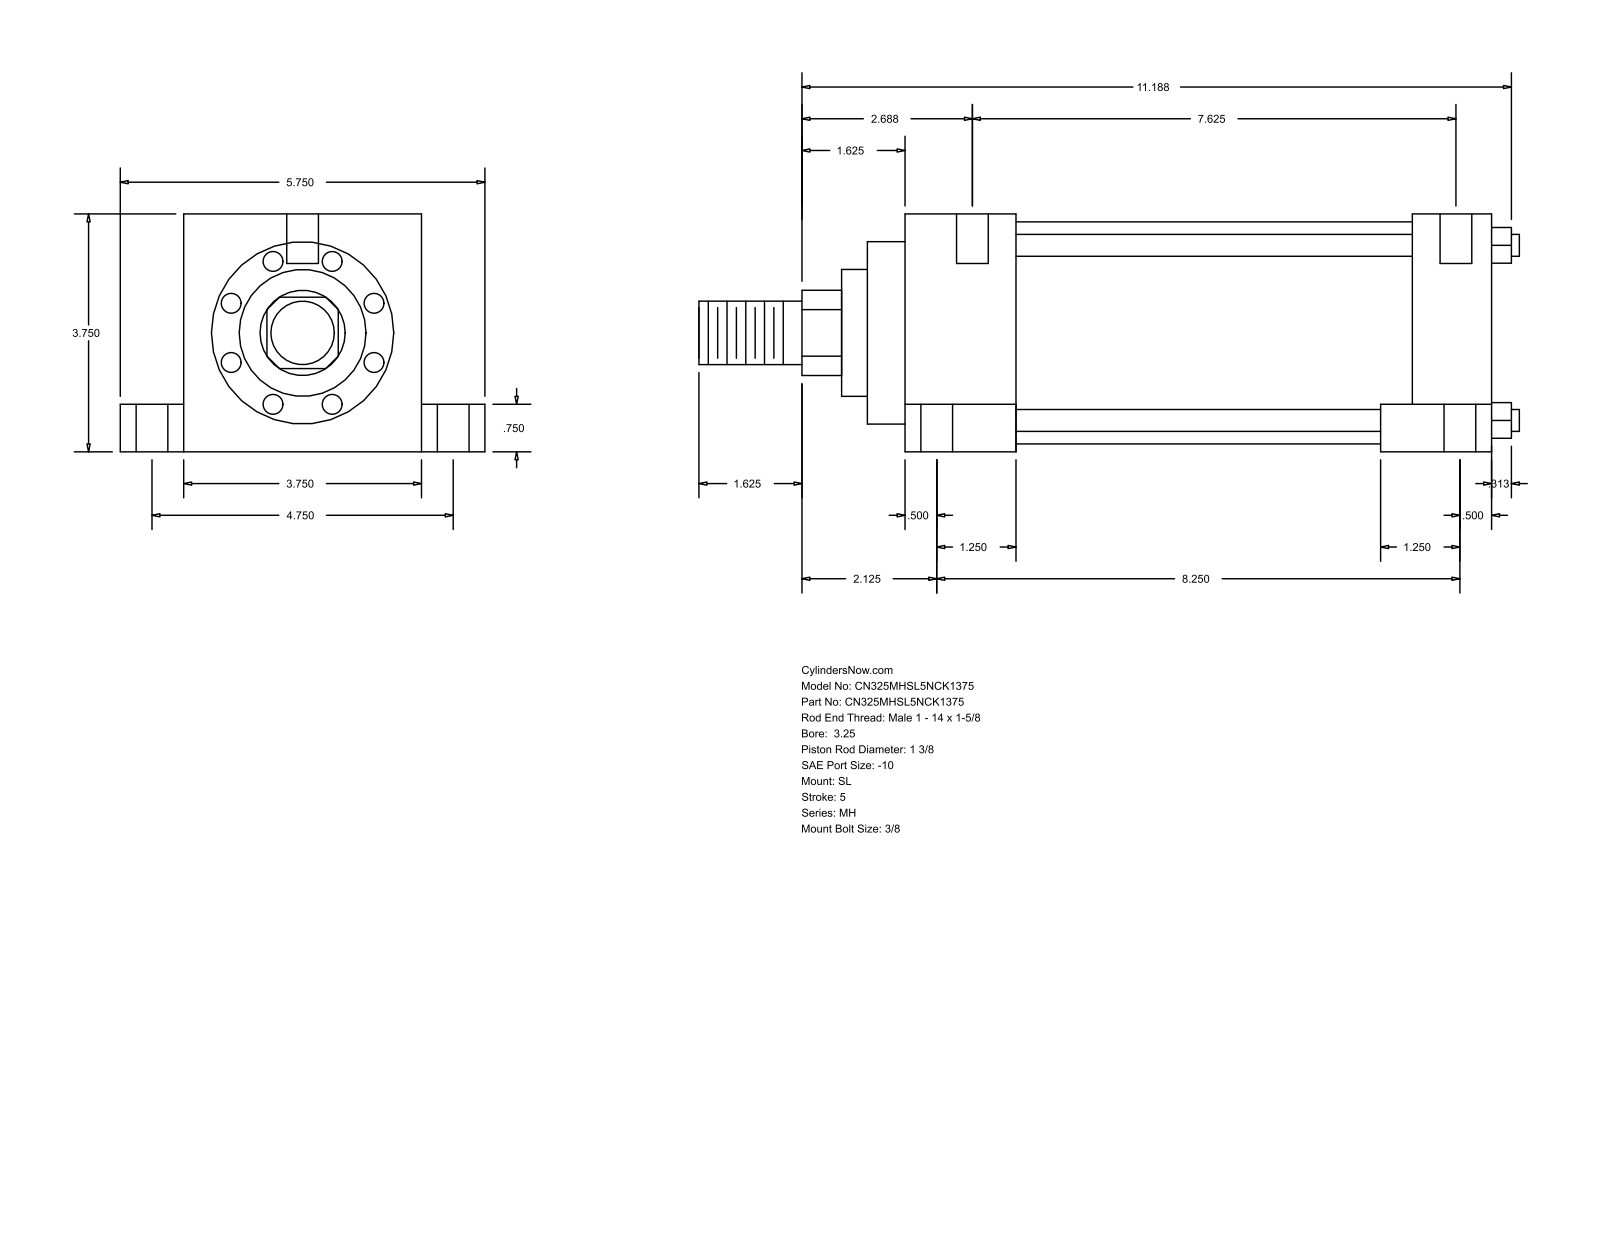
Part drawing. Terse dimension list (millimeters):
name: MH_SL__0325_1.375
written by: GSSL Pune (CONFIG_CONTROL_DESIGN)
unit: mm
bodies: 0 solids, 110 faces (77 planar, 33 cylindrical, 0 other)
size: 328.61 × 146.05 × 95.25
holes: 6× ⌀12.7, 4× ⌀5.56, 4× ⌀19.05
bosses: 4× ⌀8.76, 1× ⌀88.9, 1× ⌀73.03, 1× ⌀50.8, 1× ⌀34.92, 1× ⌀25.4
rounds: 1× R17.06
face distances: 95.24, 234.96, 44.45, 190.51, 25.41, 120.65, 19.05, 76.19, 146.06, 203.2
hole spacings: 60.35, 60.41, 61.65, 62, 120.66, 200.03, 204.37, 205.89
